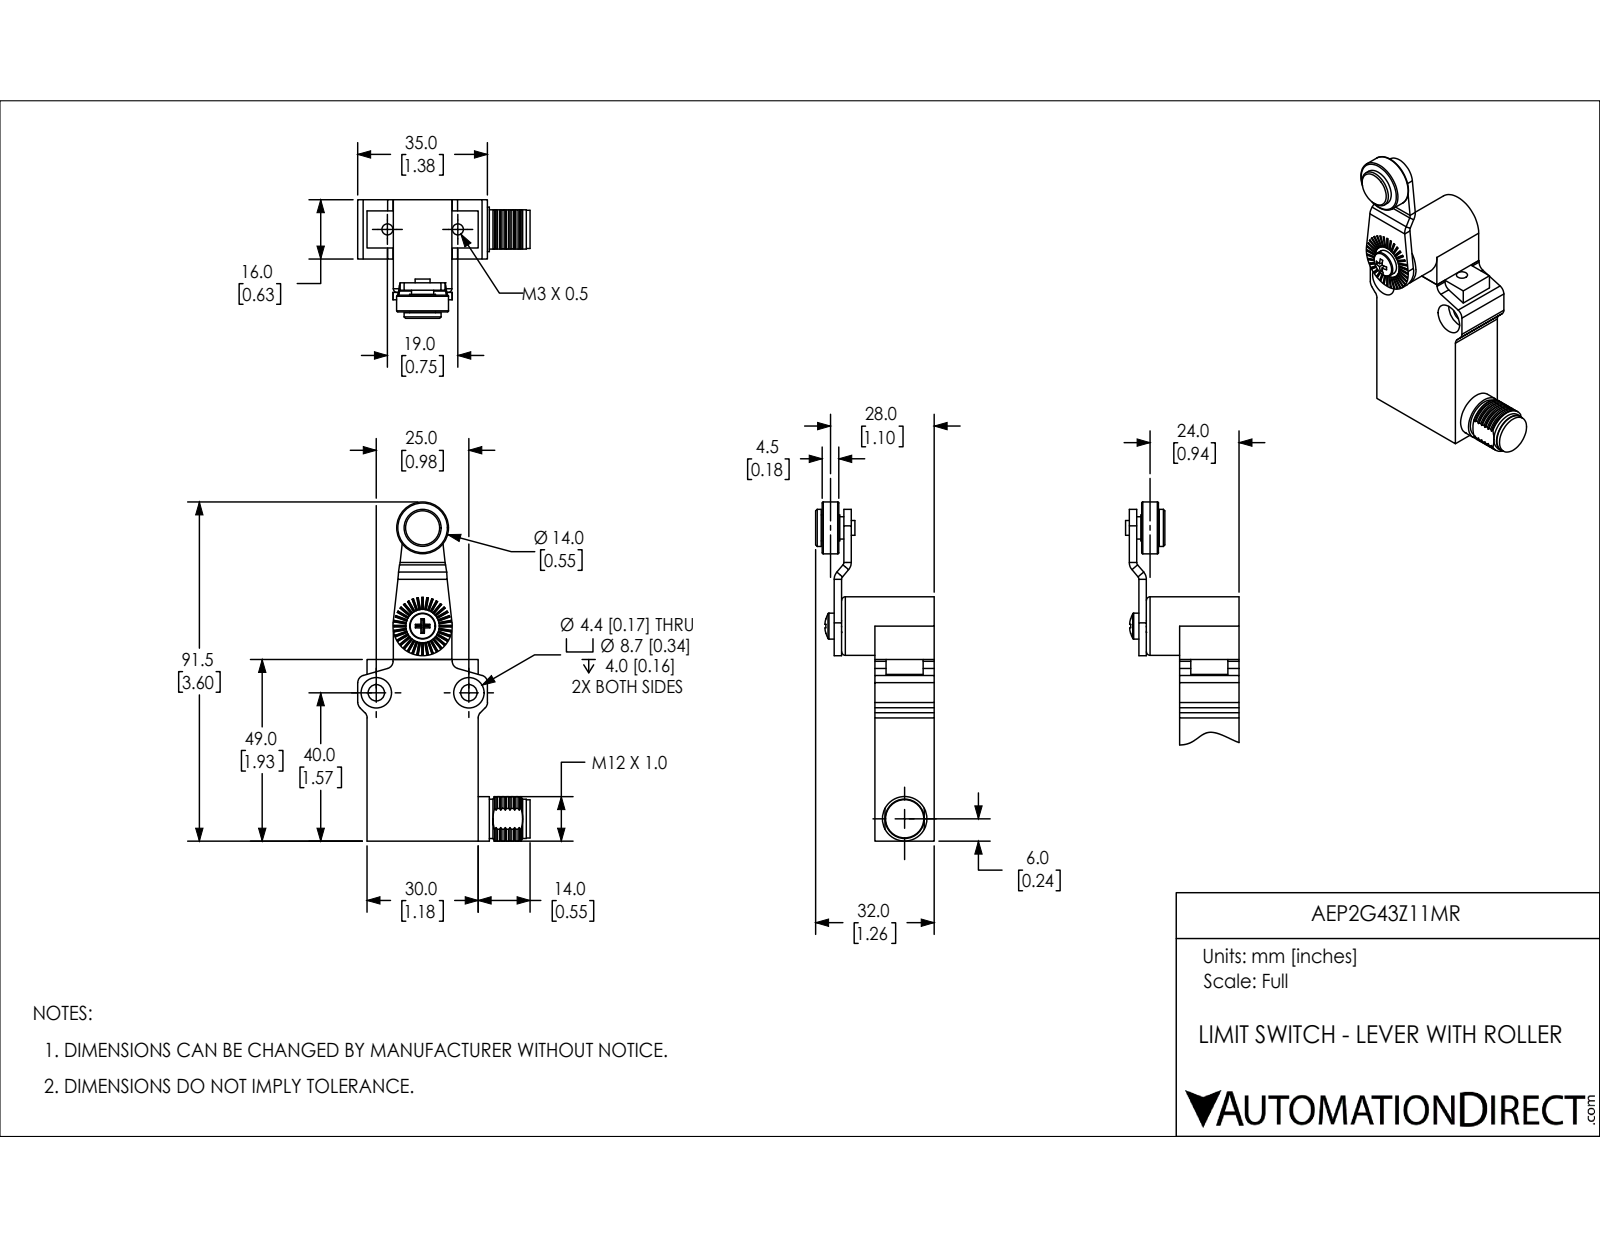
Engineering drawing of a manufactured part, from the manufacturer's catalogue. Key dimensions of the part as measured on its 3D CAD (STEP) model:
Part name (STEP PRODUCT): AEP2G43Z11MR
STEP written by: SolidWorks 2018 (AUTOMOTIVE_DESIGN)
Units: inches
Bodies: 0 solids, 658 faces (299 planar, 147 cylindrical, 212 other)
Overall size (bounding box): 3.602 × 1.831 × 1.26
Round holes (diameter × count): ⌀0.118 ×2, ⌀0.173 ×2, ⌀0.323 ×2, ⌀0.098 ×1, ⌀0.161 ×1, ⌀0.197 ×1, ⌀0.224 ×1
Round bosses / shafts (diameter × count): ⌀0.276 ×2, ⌀0.622 ×1, ⌀0.551 ×1, ⌀0.472 ×1, ⌀0.417 ×1, ⌀0.406 ×1, ⌀0.394 ×1, ⌀0.236 ×1
Partial cylindrical surfaces — rounded edges, fillets, slot ends (radius × count): R0.079 ×8, R0.039 ×2, R0.118 ×2, R0.256 ×1, R0.315 ×1
Main face-to-face distances: 0.63, 1.181, 1.929, 0.354, 0.079, 0.984, 0.28, 0.902, 0.102, 0.472
Hole centre spacings: 0.863, 1.82, 0.748, 0.984, 1.043
